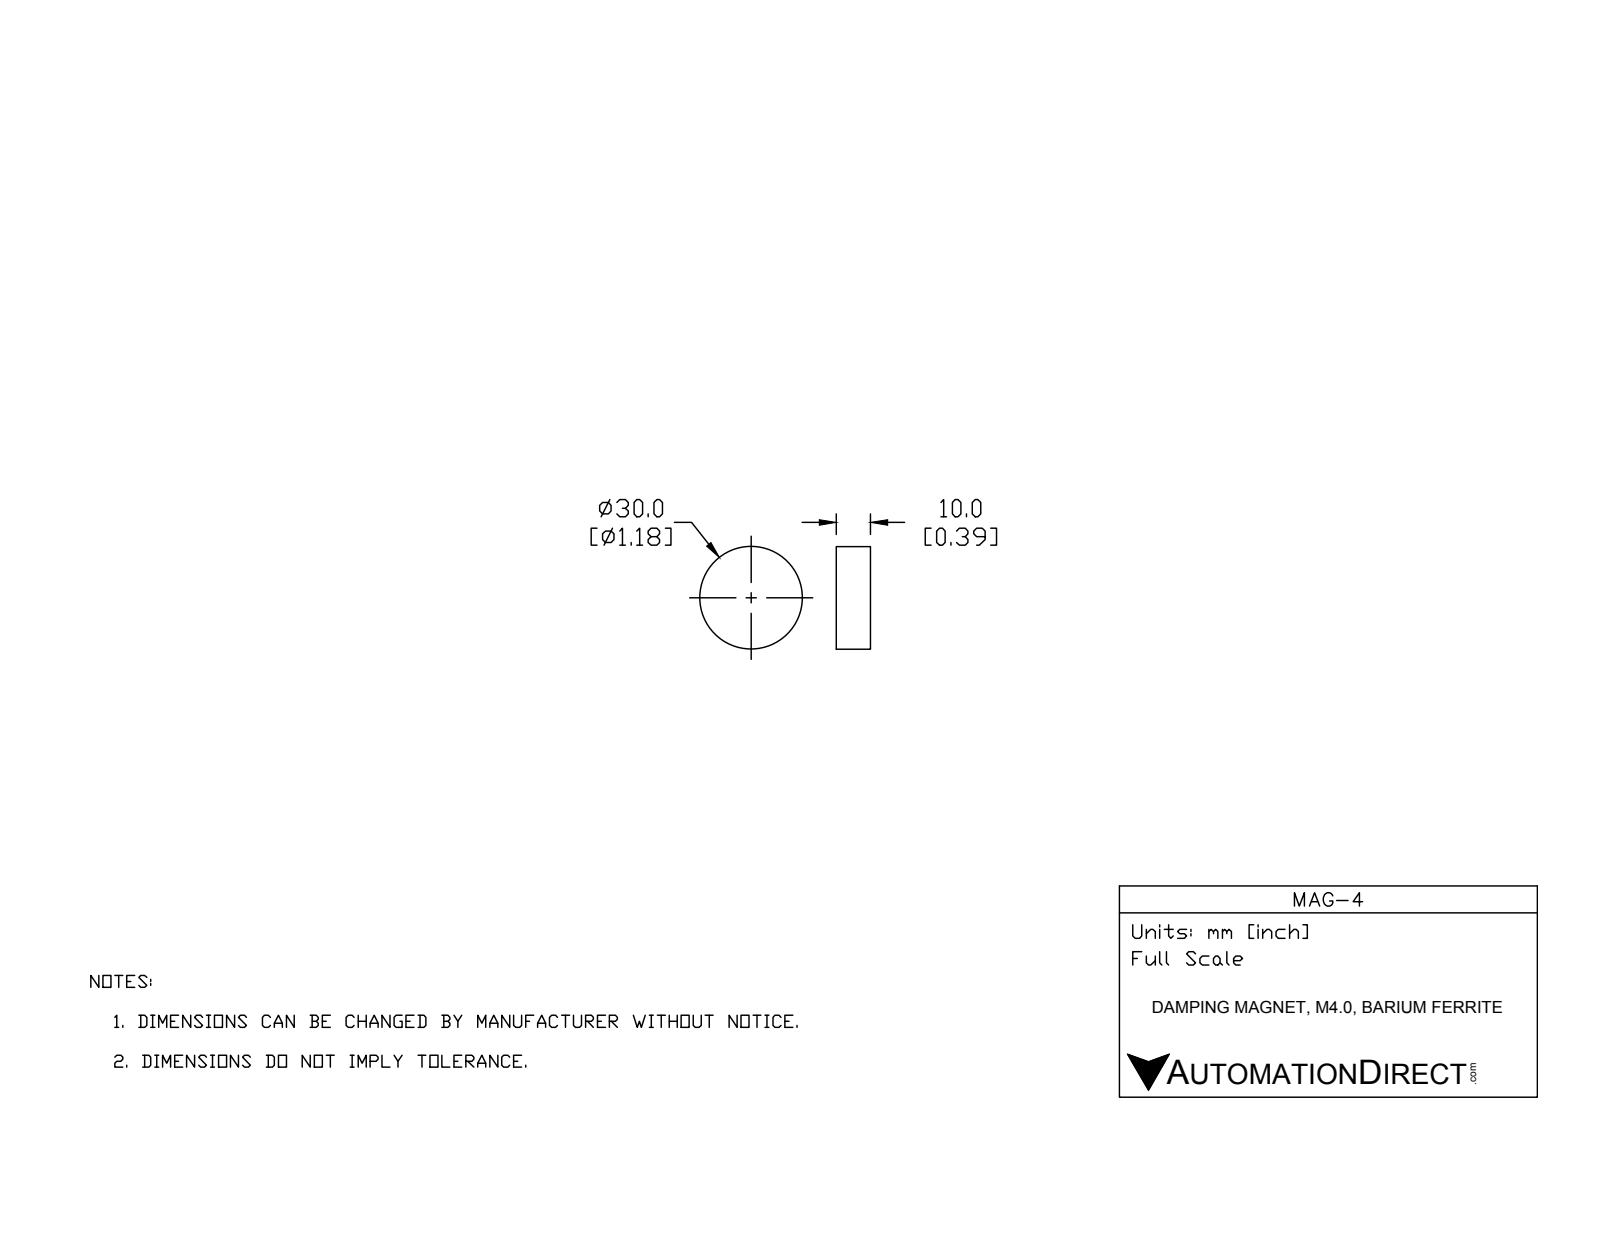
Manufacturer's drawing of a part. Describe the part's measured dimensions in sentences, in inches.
The part is named "MAG-4". Its 3-D file was written by "SolidWorks 2017 (AUTOMOTIVE_DESIGN)". It is 1 solid with 4 faces: 2 planar, 2 cylindrical and 0 other. Overall it measures 1.181 by 1.181 by 0.394 inches. Its volume is 0.431 cubic inches and its surface area 3.652 square inches. Round bosses or shafts: 1 of diameter 1.181. The main face-to-face distances are 0.394.
